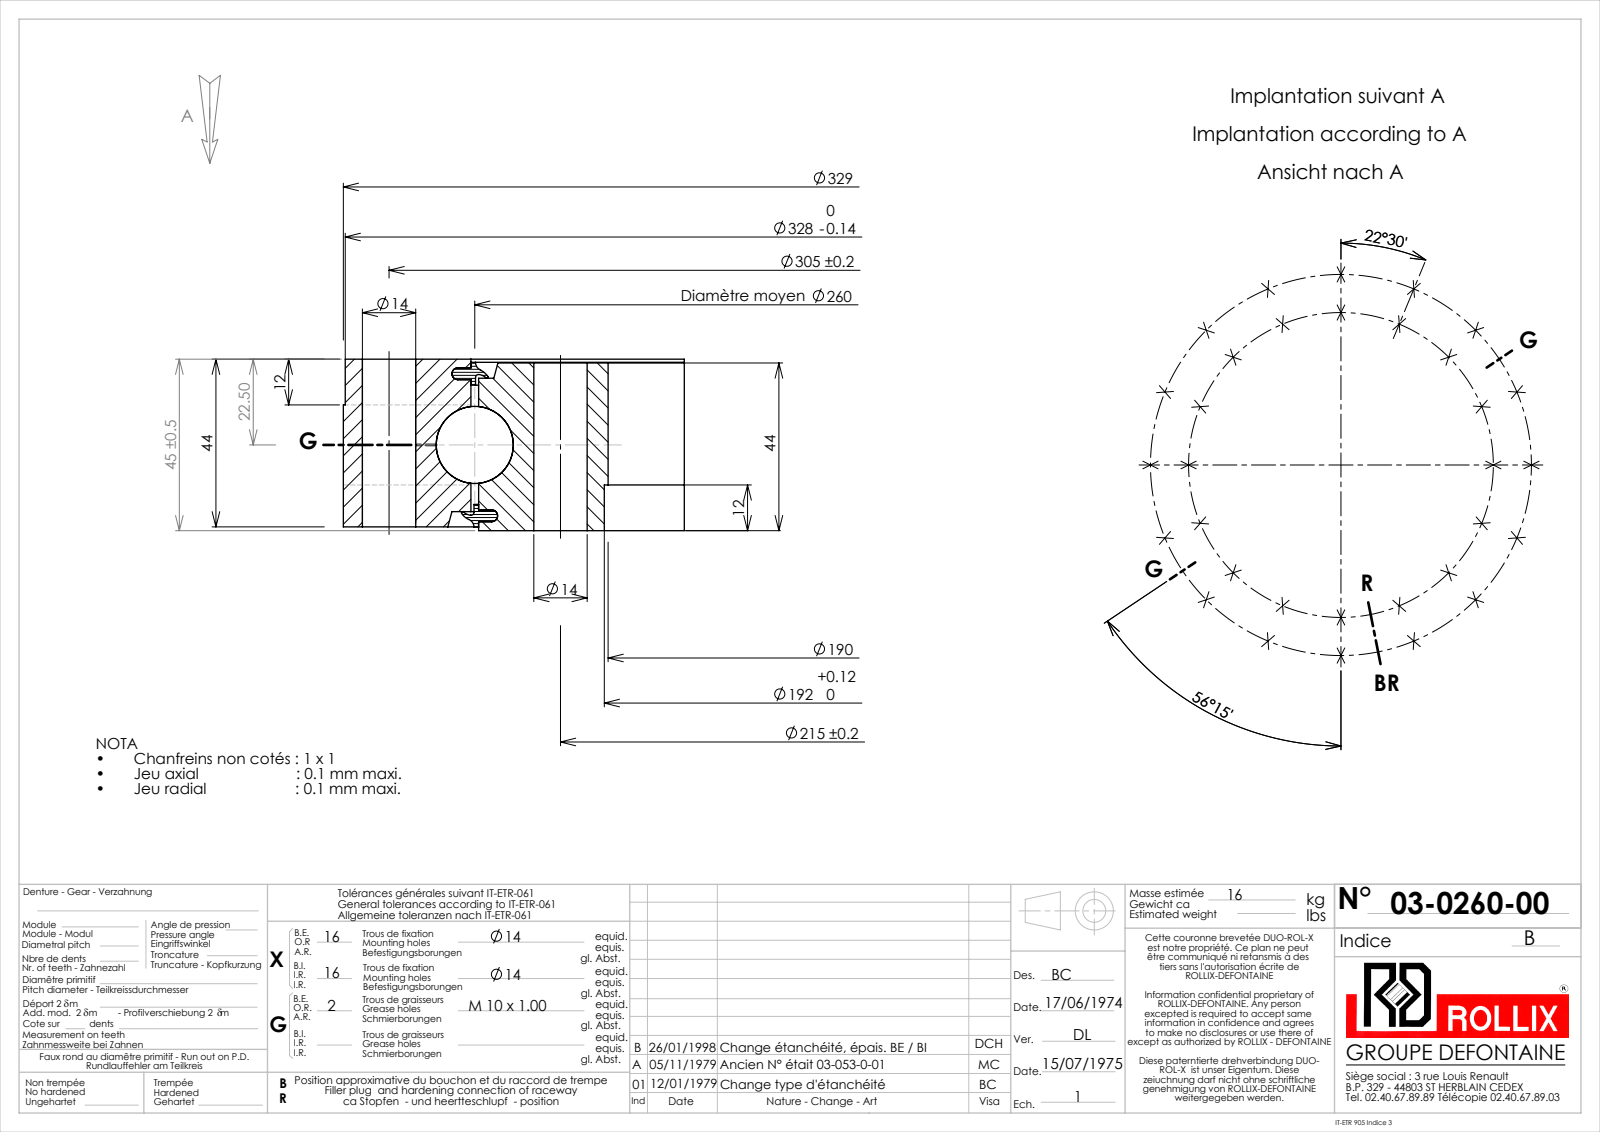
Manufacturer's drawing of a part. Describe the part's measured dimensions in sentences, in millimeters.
The part is named "03-0260-00". Its 3-D file was written by "SolidWorks 2016 (CONFIG_CONTROL_DESIGN)". It is 5 solids with 166 faces: 20 planar, 100 cylindrical and 46 other. Overall it measures 329 by 329 by 45 millimeters. Its volume is 1 948 000 cubic millimeters and its surface area 383 227 square millimeters. Round holes: 32 of diameter 14, 2 of diameter 9, 1 of diameter 190, 1 of diameter 192, 1 of diameter 258, 1 of diameter 259.6, 1 of diameter 262.02. Round bosses or shafts: 1 of diameter 329, 1 of diameter 328, 1 of diameter 262, 1 of diameter 260.4, 1 of diameter 257.97. The main face-to-face distances are 44, 1, 45, 43, 37.27, 3.1, 5, 40, 4, 39. The hole center spacings are 107.83, 67.24, 149.21, 186.58, 217.62, 255.15, 119.45, 210.87.
